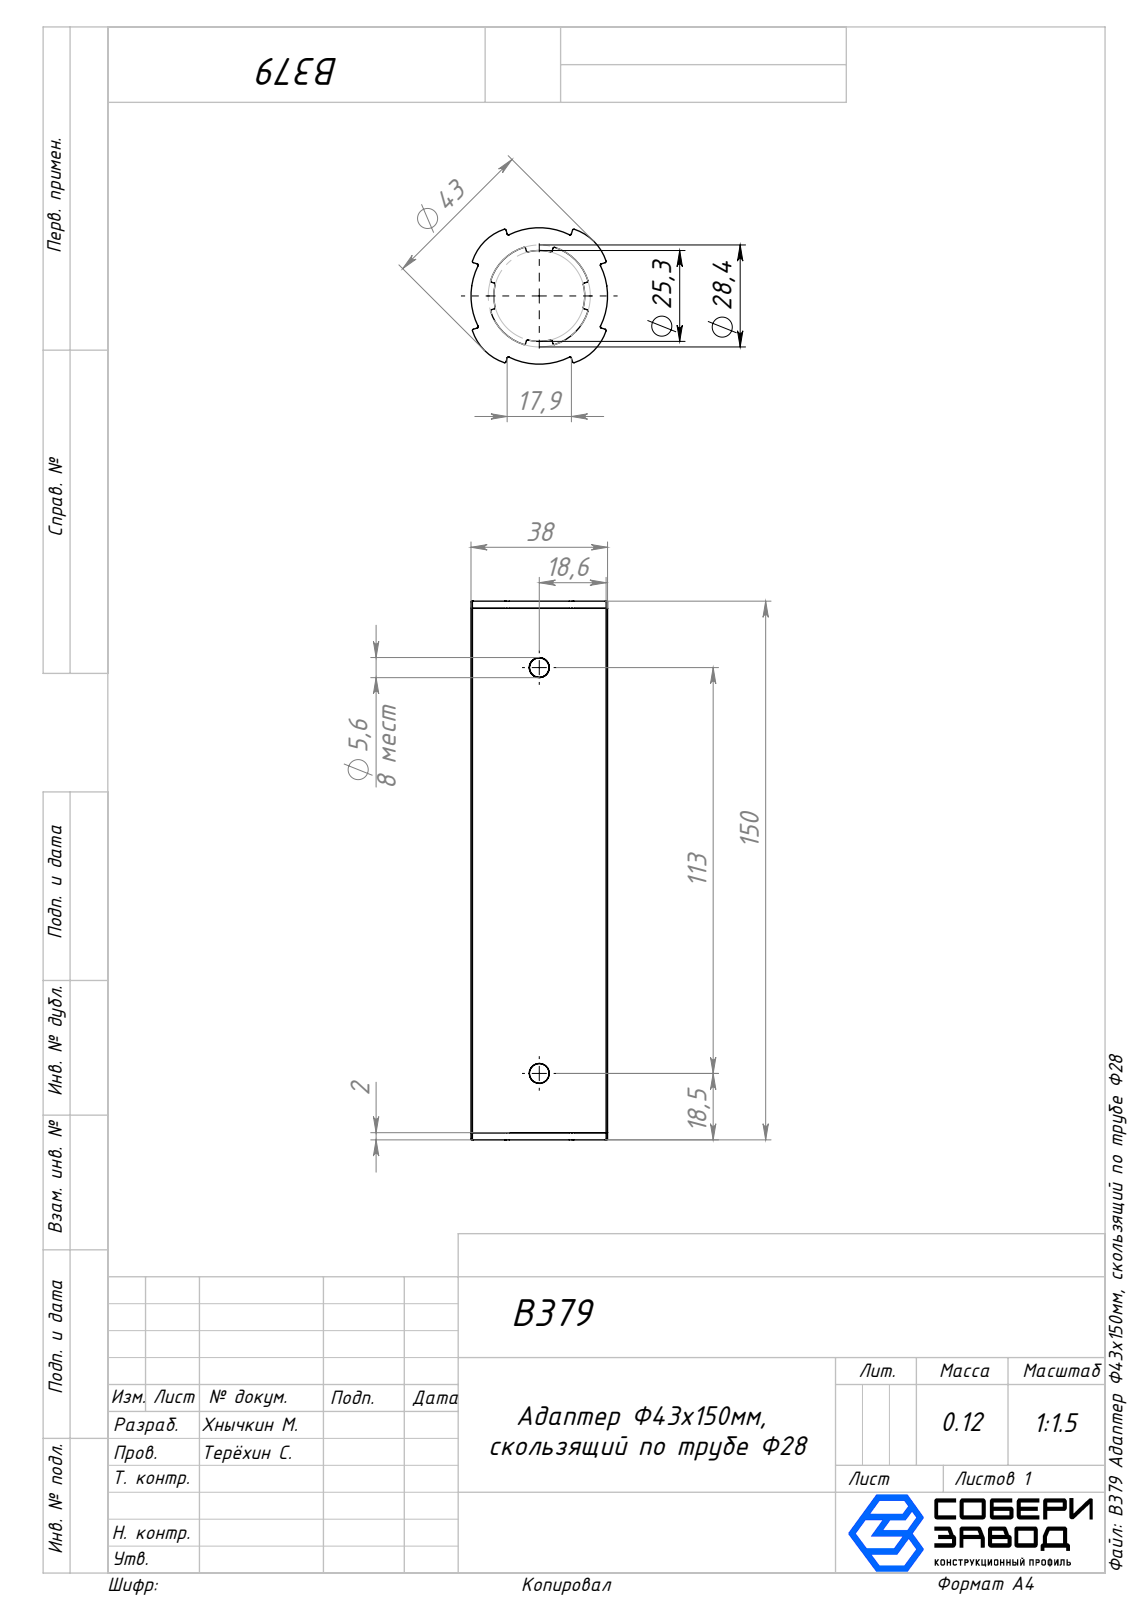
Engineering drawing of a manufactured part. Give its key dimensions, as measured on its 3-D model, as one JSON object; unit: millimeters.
{"part_name": "Корпус_00; B379 Адаптер Ф43х150мм, скользящий по трубе Ф28; Крышка_00", "step_written_by": "SolidWorks 2025 (AUTOMOTIVE_DESIGN)", "units": "millimeters", "bodies": {"solids": 3, "faces": 686, "planar": 176, "cylindrical": 370, "other": 140}, "overall_size": [150, 38, 38], "volume_mm3": 47816, "surface_area_mm2": 48035, "round_holes": [[5.6, 2], [30, 1]], "partial_cylinders_radius": [[0.35, 40], [0.45, 36], [0.2, 32], [0.4, 16], [1, 12], [14, 4], [16.8, 3], [12.65, 1]], "face_to_face_distances": [2, 20.59, 148, 146, 150, 7.08, 137, 13, 11, 135], "hole_center_spacings": [113]}
